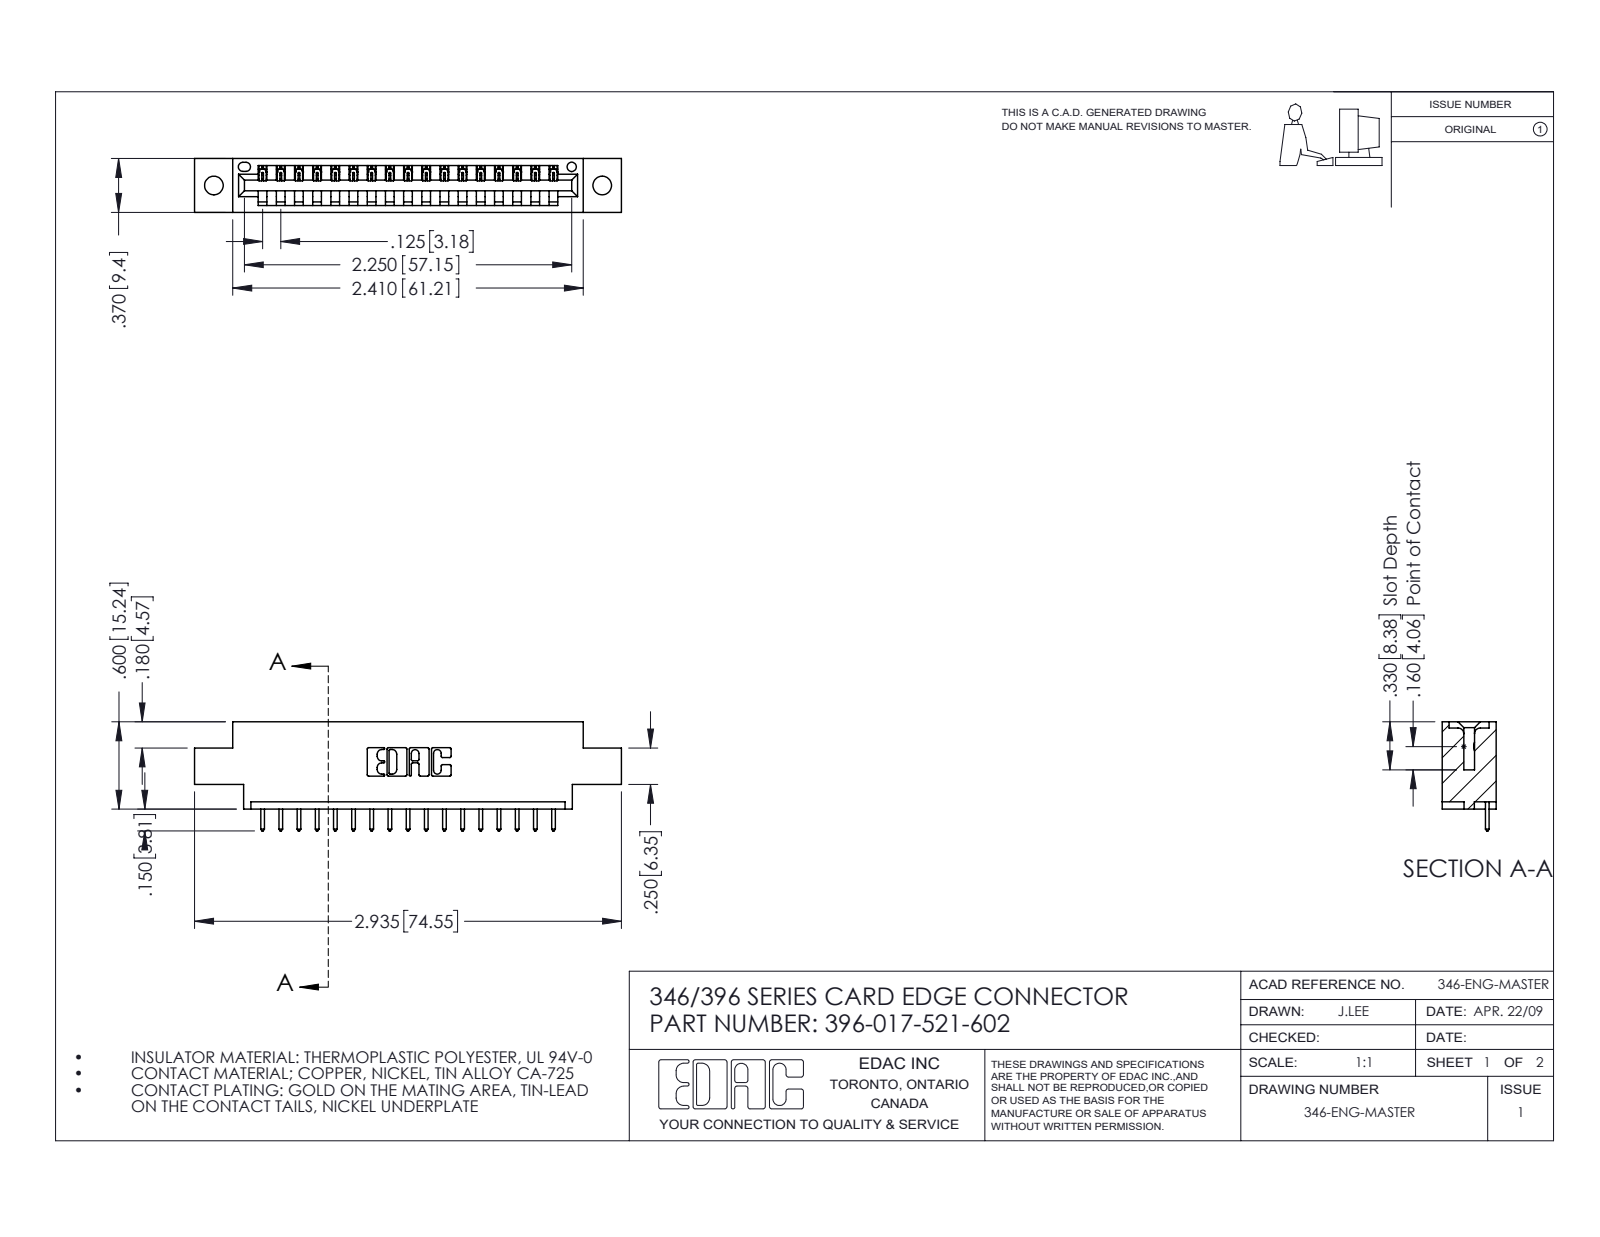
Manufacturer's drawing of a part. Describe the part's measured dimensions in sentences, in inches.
The part is named "346 Part_0.170 Offset - 0.128 Dia; 396-017-521-602; 345-292-001_345-293-121". Its 3-D file was written by "SolidWorks 2016 (CONFIG_CONTROL_DESIGN)". It is 18 solids with 1112 faces: 760 planar, 352 cylindrical and 0 other. Overall it measures 2.935 by 0.75 by 0.37 inches. Its volume is 0.41 cubic inches and its surface area 12.14 square inches. Round holes: 2 of diameter 0.128, 1 of diameter 0.064. Partial cylindrical surfaces (rounded edges, fillets, slot ends): 34 of radius 0.006, 34 of radius 0.01, 22 of radius 0.01, 6 of radius 0.007, 6 of radius 0.031, 3 of radius 0.026, 2 of radius 0.031, 2 of radius 0.04. The main face-to-face distances are 0.37, 0.048, 0.322, 0.25, 0.072, 0.298, 0.025, 0.148, 0.222, 0.1. The hole center spacings are 0.246, 2.463, 2.67.
